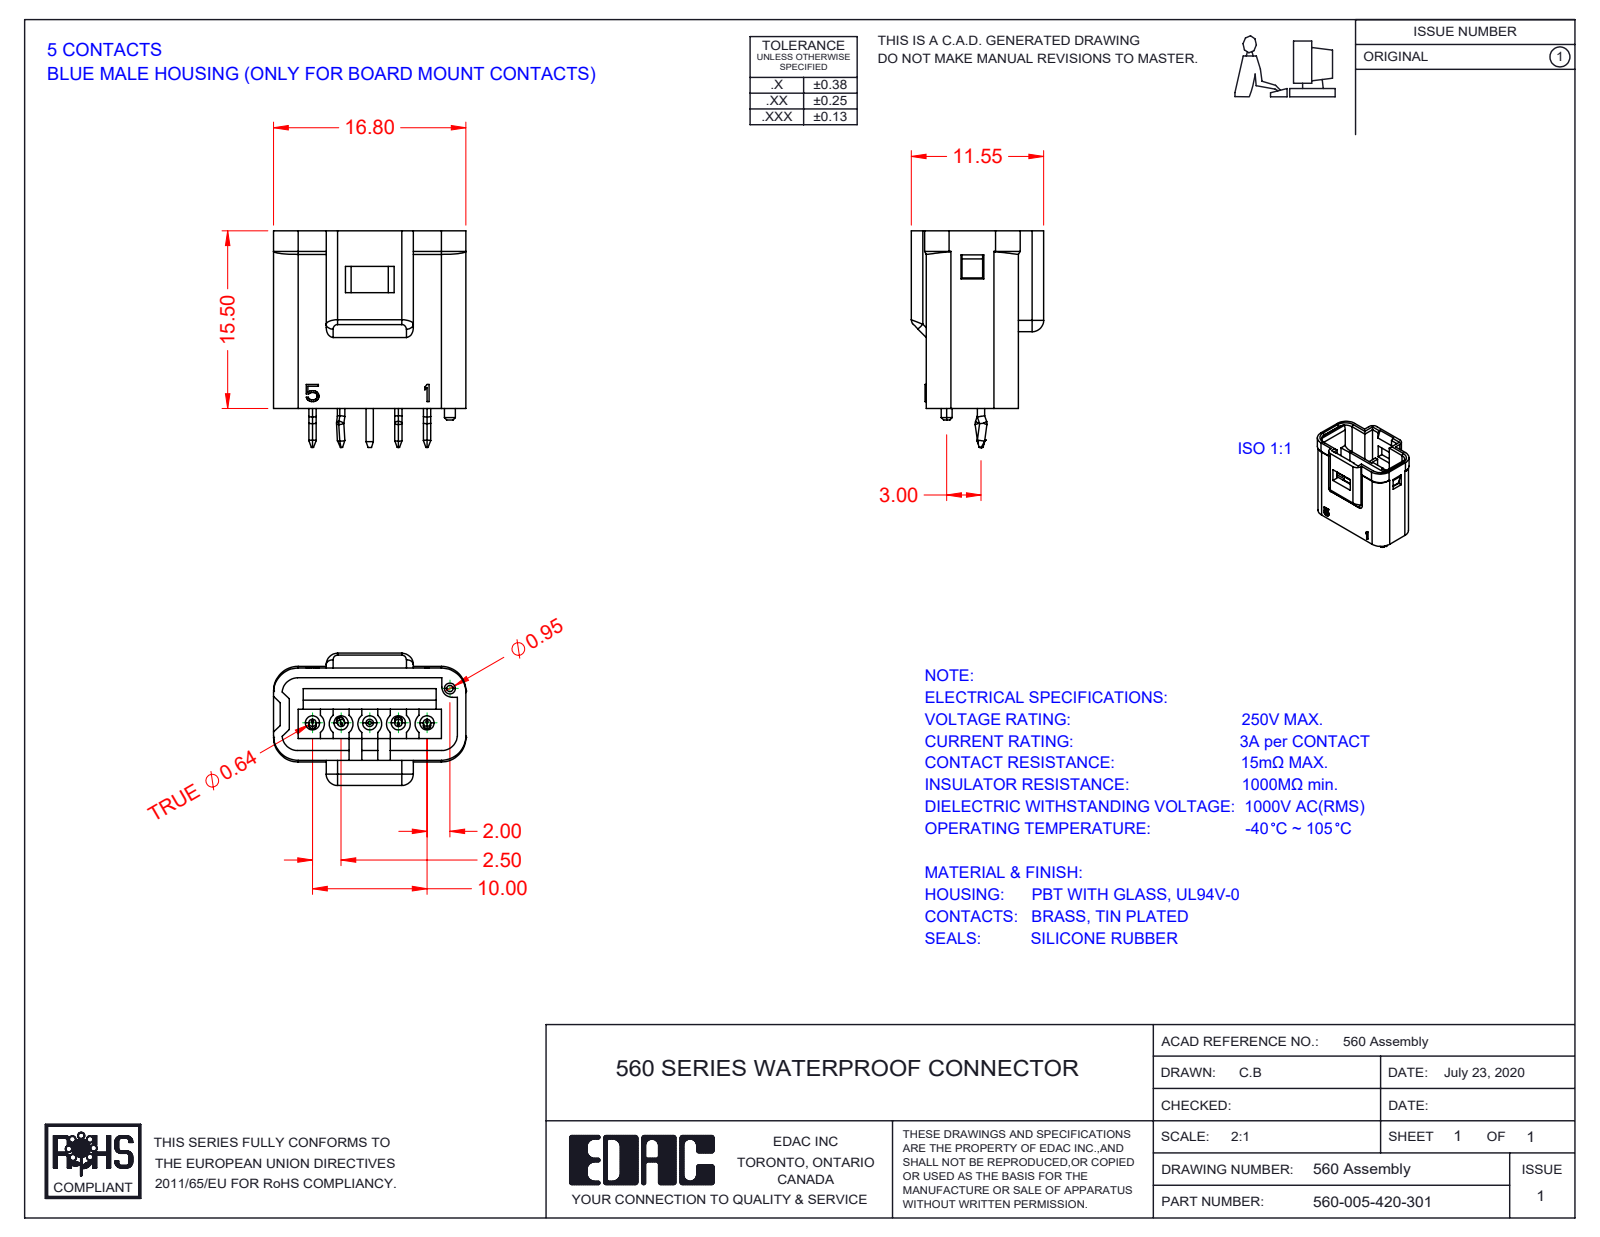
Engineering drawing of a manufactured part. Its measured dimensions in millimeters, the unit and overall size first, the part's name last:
Units: millimetres
Overall size (bounding box): 18.9 × 16.8 × 11.55
Round holes (diameter × count): ⌀0.64 ×5, ⌀1.4 ×5, ⌀1.1 ×1
Round bosses / shafts (diameter × count): ⌀0.64 ×8, ⌀0.95 ×1
Partial cylindrical surfaces — rounded edges, fillets, slot ends (radius × count): R1 ×25, R0.25 ×16, R0.35 ×12, R1.65 ×8, R2.15 ×8, R0.3 ×4, R0.5 ×4, R1.1 ×4
Main face-to-face distances: 0.6, 7.45, 3.6, 8.05, 1.1, 7.4, 6.8, 1.9, 6.85, 2.5
Hole centre spacings: 2.5, 5, 3.14, 5.35, 7.5, 1.9, 10
Volume: 1 028 mm³ · Surface area: 2 869 mm²
Bodies: 8 solids, 772 faces (448 planar, 184 cylindrical, 140 other)
Part name (STEP PRODUCT): INTERNAL-WIRE-SEAL-5POS; PCB-HEADER-CONTACT-5P; FACIAL_SEAL_5POS; CONTACT_PCB-HEADER-1 (+5 more)
STEP written by: SolidWorks 2020 (CONFIG_CONTROL_DESIGN)
